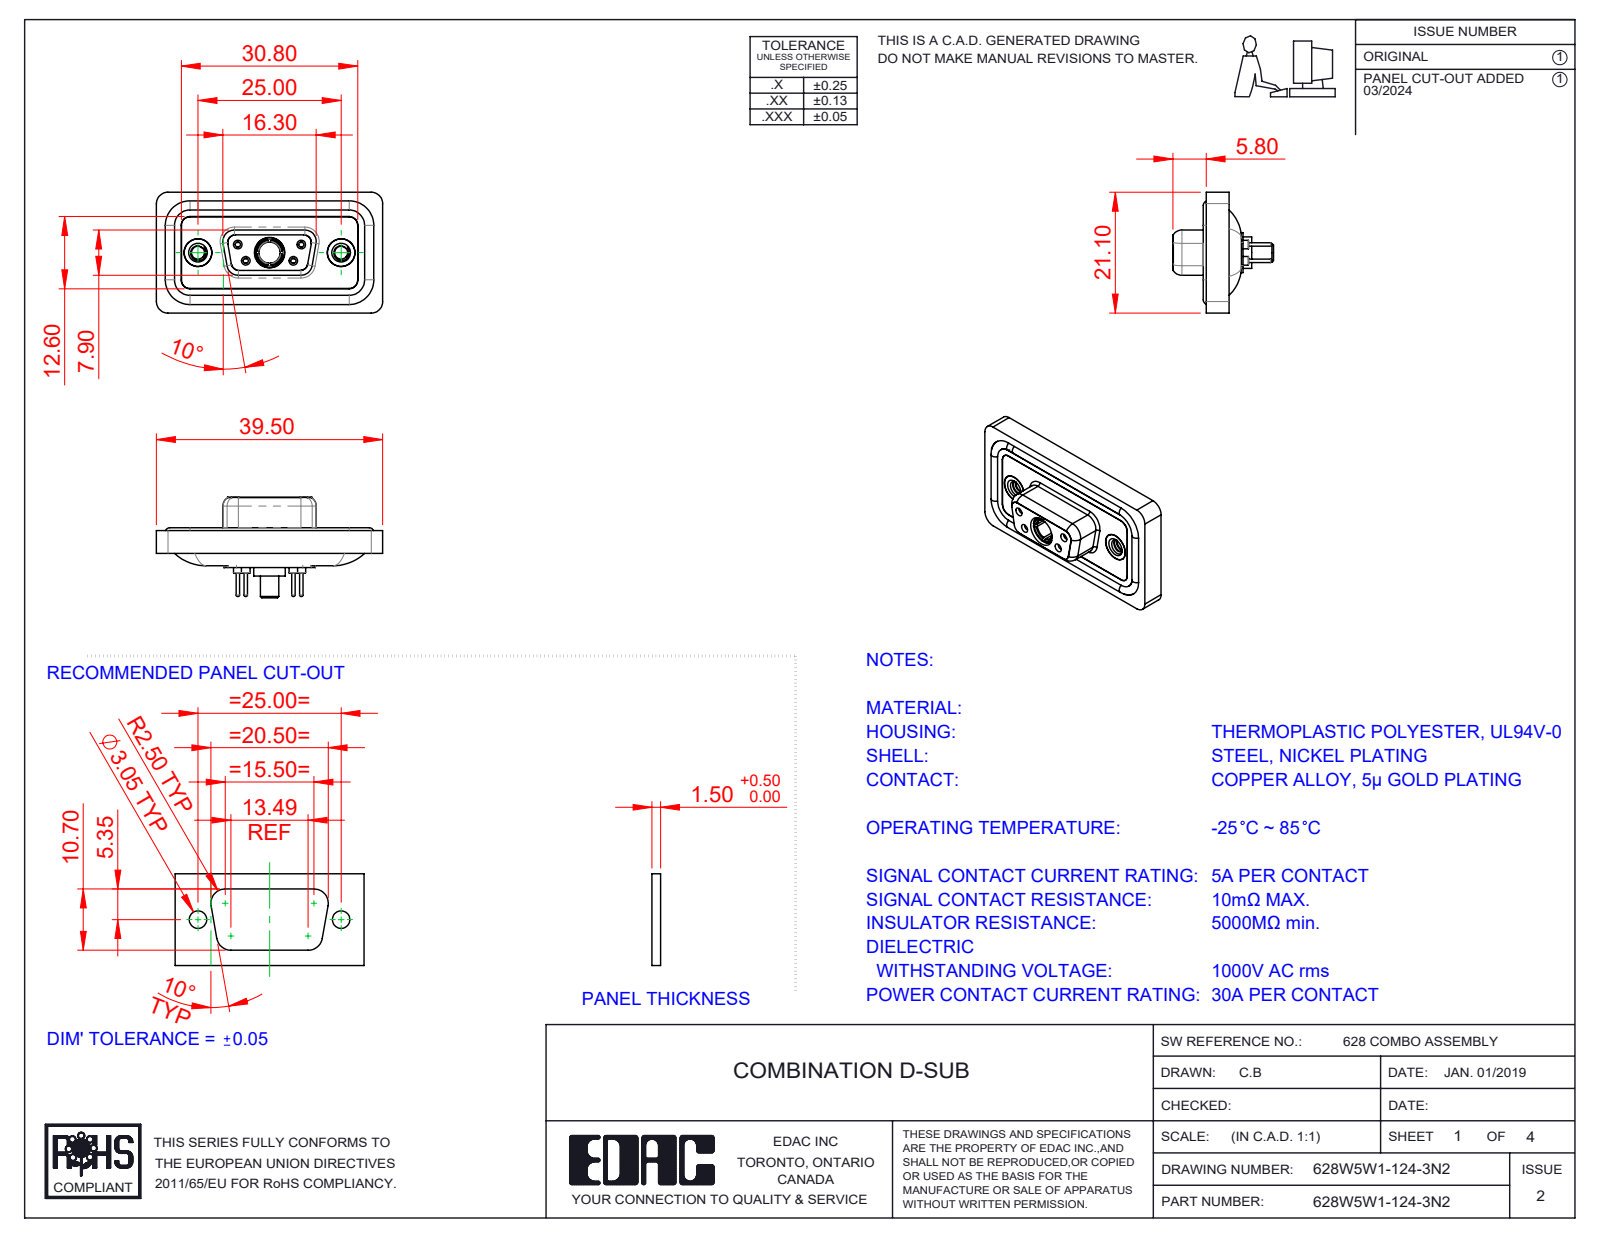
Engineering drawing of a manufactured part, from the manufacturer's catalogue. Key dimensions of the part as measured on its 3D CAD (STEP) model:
Part name (STEP PRODUCT): 628Combo Contact Row 1_24; Power Socket_30A S; 628Combo Contact Row 2_24; 628Combo Waterproof Housing_09 Contacts (+5 more)
STEP written by: SolidWorks 2023 (CONFIG_CONTROL_DESIGN)
Units: millimetres
Bodies: 13 solids, 680 faces (194 planar, 287 cylindrical, 199 other)
Overall size (bounding box): 39.5 × 21.1 × 17.55
Volume: 4 774 mm³ · Surface area: 7 640 mm²
Round holes (diameter × count): ⌀0.9 ×4, ⌀1.1 ×4, ⌀1.5 ×4, ⌀2 ×4, ⌀4.85 ×3, ⌀1.6 ×2, ⌀1.7 ×2, ⌀2.26 ×2, ⌀4 ×2, ⌀4.05 ×2, ⌀5 ×2, ⌀3.7 ×1
Round bosses / shafts (diameter × count): ⌀1.6 ×6, ⌀2.2 ×4, ⌀0.6 ×4, ⌀4.95 ×2, ⌀4.8 ×2, ⌀5.5 ×1, ⌀5.2 ×1, ⌀4.96 ×1
Partial cylindrical surfaces — rounded edges, fillets, slot ends (radius × count): R1.5 ×22, R2 ×18, R1.35 ×8, R1.6 ×8, R0.25 ×4, R0.5 ×4, R0.6 ×4, R0.65 ×4
Main face-to-face distances: 0.4, 2.9, 1.1, 1.8, 1.6, 0.5, 5.65, 7.45, 5.35, 3.6
Hole centre spacings: 3.16, 5.72, 7.1, 12.5, 18.1, 4.39, 4.4, 8.31
